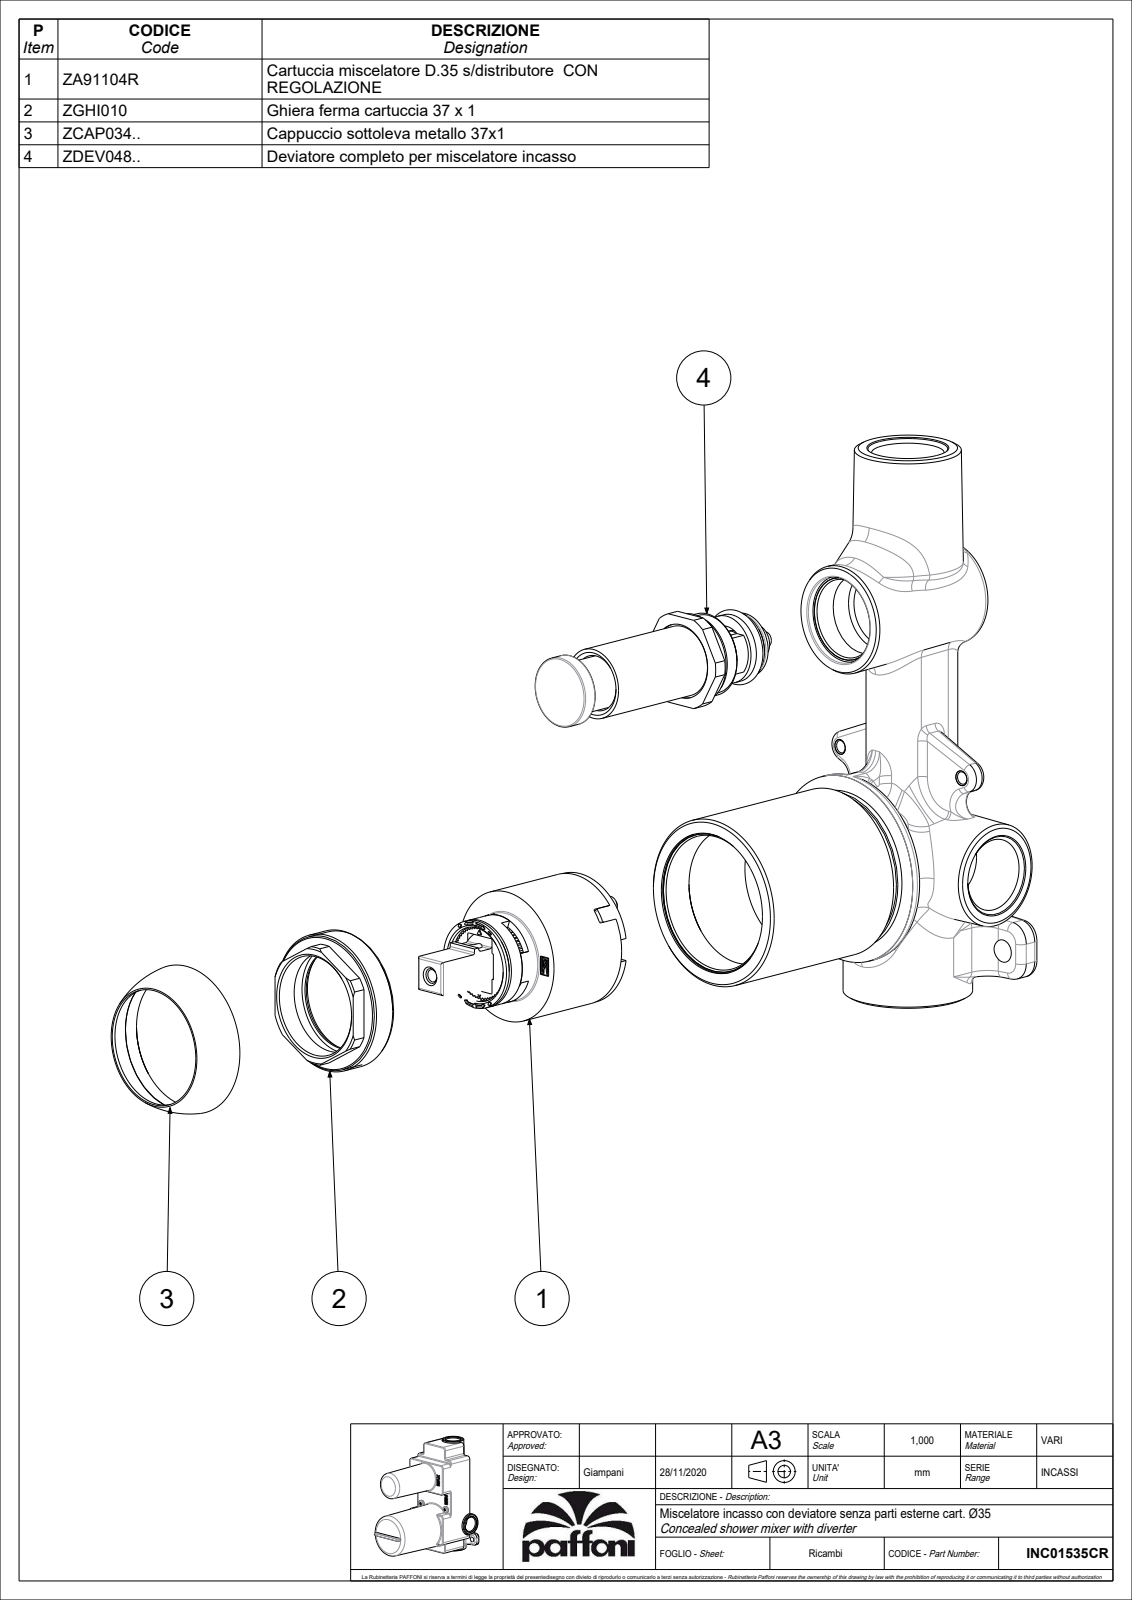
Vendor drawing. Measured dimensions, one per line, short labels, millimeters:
name: INC01535CR
written by: CREO PARAMETRIC BY PTC INC, 2020044 (CONFIG_CONTROL_DESIGN)
unit: mm
bodies: 1 solid, 2031 faces (805 planar, 547 cylindrical, 679 other)
size: 148 × 143.3 × 66
volume: 268 035 mm³; area: 166 087 mm²
holes: 5× ⌀8, 3× ⌀6, 3× ⌀7, 3× ⌀9.5, 3× ⌀19, 2× ⌀4, 2× ⌀4.2, 1× ⌀3.3, 1× ⌀4.1, 1× ⌀4.3, 1× ⌀5, 1× ⌀10.5
bosses: 3× ⌀4, 2× ⌀8, 2× ⌀7.8, 1× ⌀50, 1× ⌀44.8, 1× ⌀42, 1× ⌀35, 1× ⌀34.8
rounds: 53× R2, 45× R1, 35× R0.5, 22× R4, 12× R0.2, 11× R0.15, 8× R1.5, 7× R5
face distances: 2, 60, 11, 85, 13, 49, 58, 38, 62, 15
hole spacings: 8.6, 14.33, 73.33, 3.6, 7.4, 7.5, 11, 14
